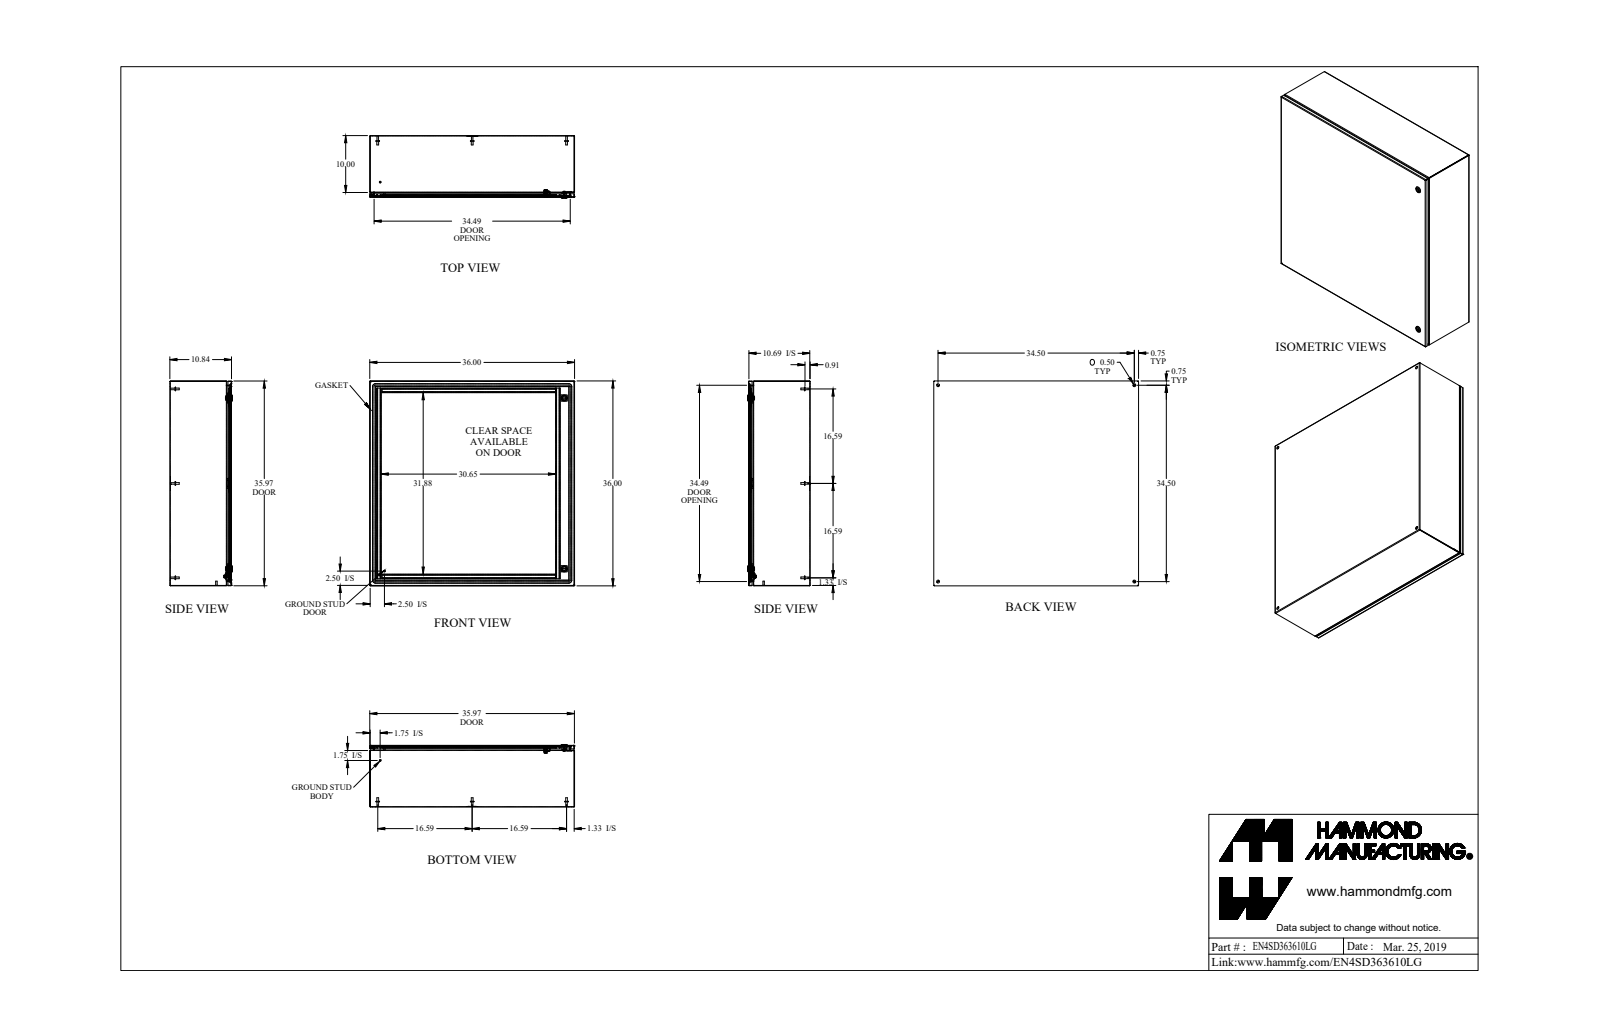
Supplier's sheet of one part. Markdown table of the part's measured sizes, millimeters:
| quantity | value |
| --- | --- |
| part name | EN4SD363610LG |
| STEP written by | SolidWorks 2019 (AUTOMOTIVE_DESIGN) |
| units | millimeters |
| bodies | 41 solids, 1184 faces (555 planar, 394 cylindrical, 235 other) |
| overall size | 914.4 × 914.4 × 279.3 |
| volume | 5 480 000 mm³ |
| surface area | 6 097 000 mm² |
| round holes (diameter × count) | 12.7 × 4, 5.9 × 2, 15.9 × 2, 19.9 × 2, 4.4 × 1, 5 × 1, 6.1 × 1, 6.1 × 1, 7 × 1, 9.5 × 1 |
| round bosses / shafts (diameter × count) | 8 × 8, 6.9 × 8, 15.9 × 6, 15.9 × 3, 27.9 × 2, 13.3 × 2, 7.1 × 2, 6.4 × 2 |
| partial cylindrical surfaces (radius × count) | 1.1 × 24, 2.1 × 24, 0.9 × 20, 2.7 × 20, 1.6 × 10, 2.4 × 10, 7.9 × 10, 0.4 × 9 |
| main face-to-face distances | 1.8, 273.4, 912.6, 271.6, 275.3, 910.7, 914.4, 21.3, 252.2, 1 |
| hole center spacings | 876.3, 851, 1239.3, 63.3, 63.3, 90, 112.8, 762 |
